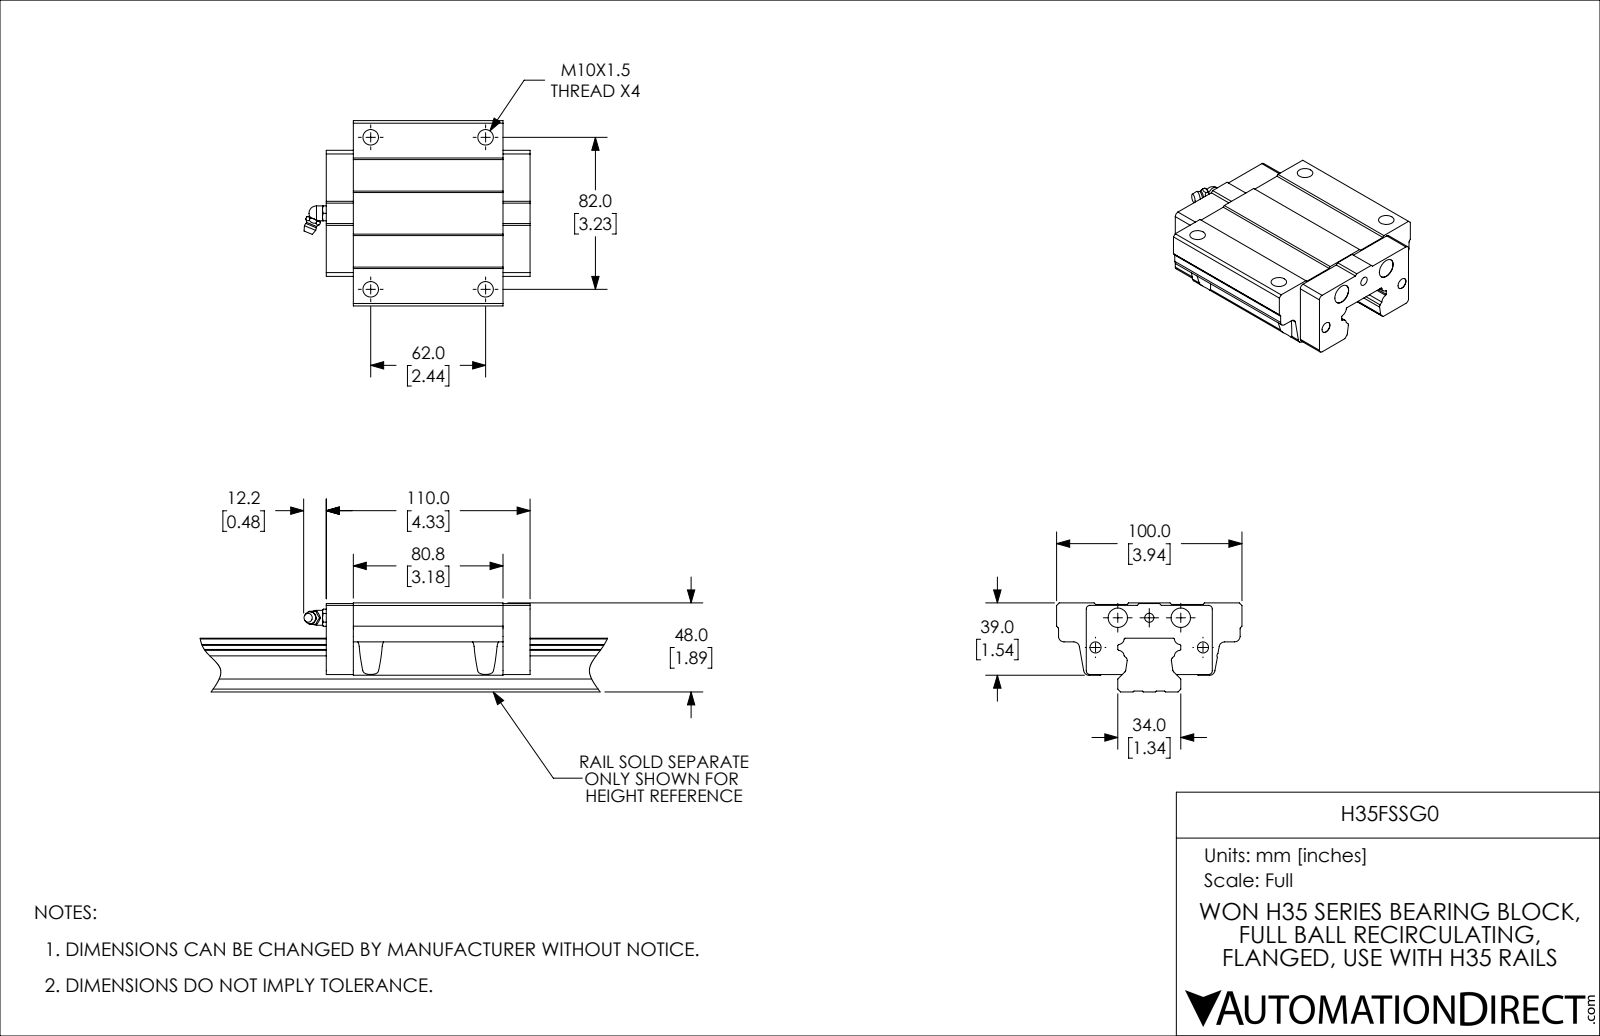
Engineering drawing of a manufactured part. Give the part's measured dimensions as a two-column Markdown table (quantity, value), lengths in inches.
| quantity | value |
| --- | --- |
| part name | H35FSSG0 |
| STEP written by | SolidWorks 2019 (CONFIG_CONTROL_DESIGN) |
| units | inches |
| bodies | 2 solids, 184 faces (93 planar, 69 cylindrical, 22 other) |
| overall size | 4.803 × 3.937 × 1.535 |
| volume | 17.05 in³ |
| surface area | 63.68 in² |
| round holes (diameter × count) | 0.33 × 4, 0.236 × 2, 0.413 × 2, 0.194 × 1 |
| round bosses / shafts (diameter × count) | 0.315 × 1, 0.236 × 1 |
| partial cylindrical surfaces (radius × count) | 0.118 × 6, 0.059 × 5, 0.079 × 4, 0.126 × 4, 0.276 × 4, 0.02 × 2, 0.039 × 2 |
| main face-to-face distances | 0.748, 0.772, 1.52, 1.488, 0.717, 0.031, 0.02, 0.63, 3.307, 4.331 |
| hole center spacings | 0.669, 0.787, 1.304, 1.917, 2.441, 3.228, 4.047, 1.339 |
